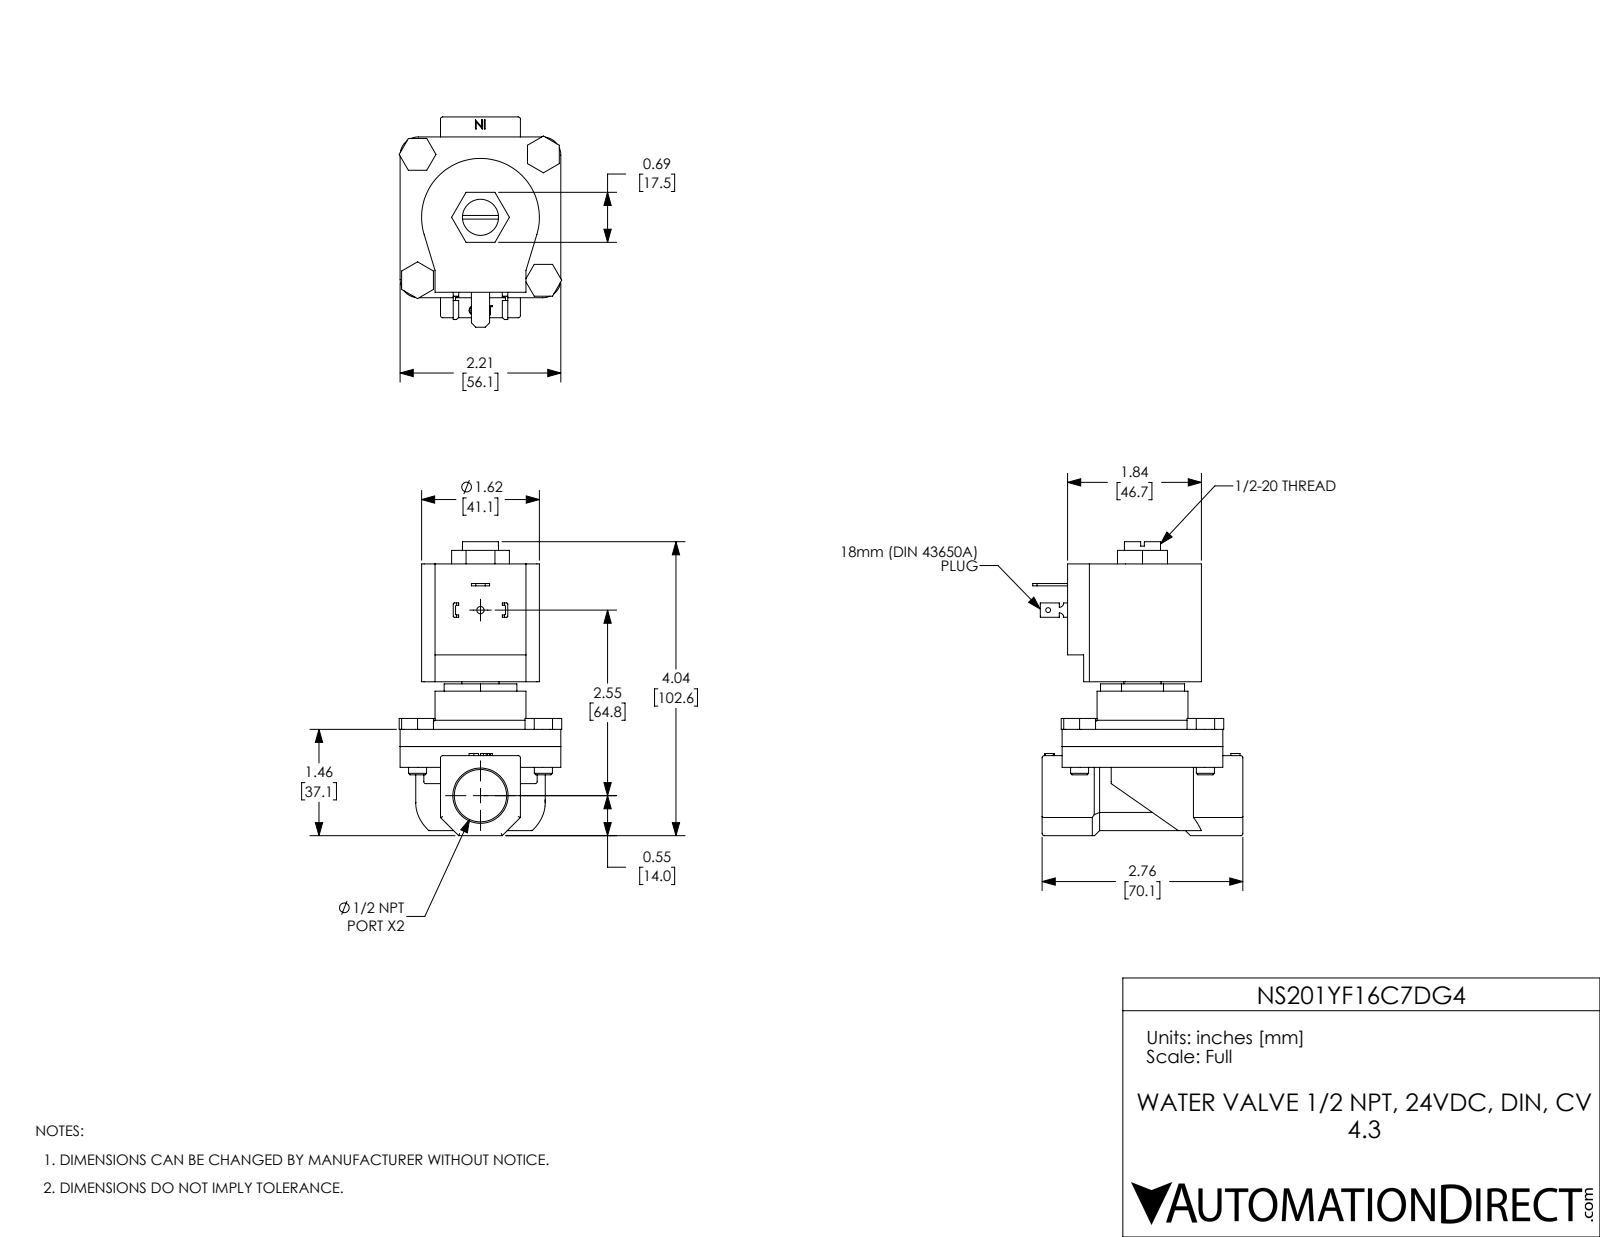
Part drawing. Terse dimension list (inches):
name: NS201YF16C7DG4
written by: SolidWorks 2021 (CONFIG_CONTROL_DESIGN)
unit: in
bodies: 11 solids, 330 faces (196 planar, 99 cylindrical, 35 other)
size: 4.04 × 2.89 × 2.235
volume: 9.842 in³; area: 63.61 in²
holes: 4× ⌀0.25, 1× ⌀0.067, 1× ⌀0.1, 1× ⌀0.496, 1× ⌀0.512, 1× ⌀0.72, 1× ⌀1.155
bosses: 4× ⌀0.248, 1× ⌀1.25
rounds: 15× R0.03, 8× R0.015, 4× R0.25, 2× R0.06, 1× R0.81, 1× R0.89
face distances: 0.237, 0.237, 2.51, 2.51, 2.273, 0.556, 1.654, 0.286, 0.286, 0.523
hole spacings: 1.223, 1.73, 2.446, 2.55
